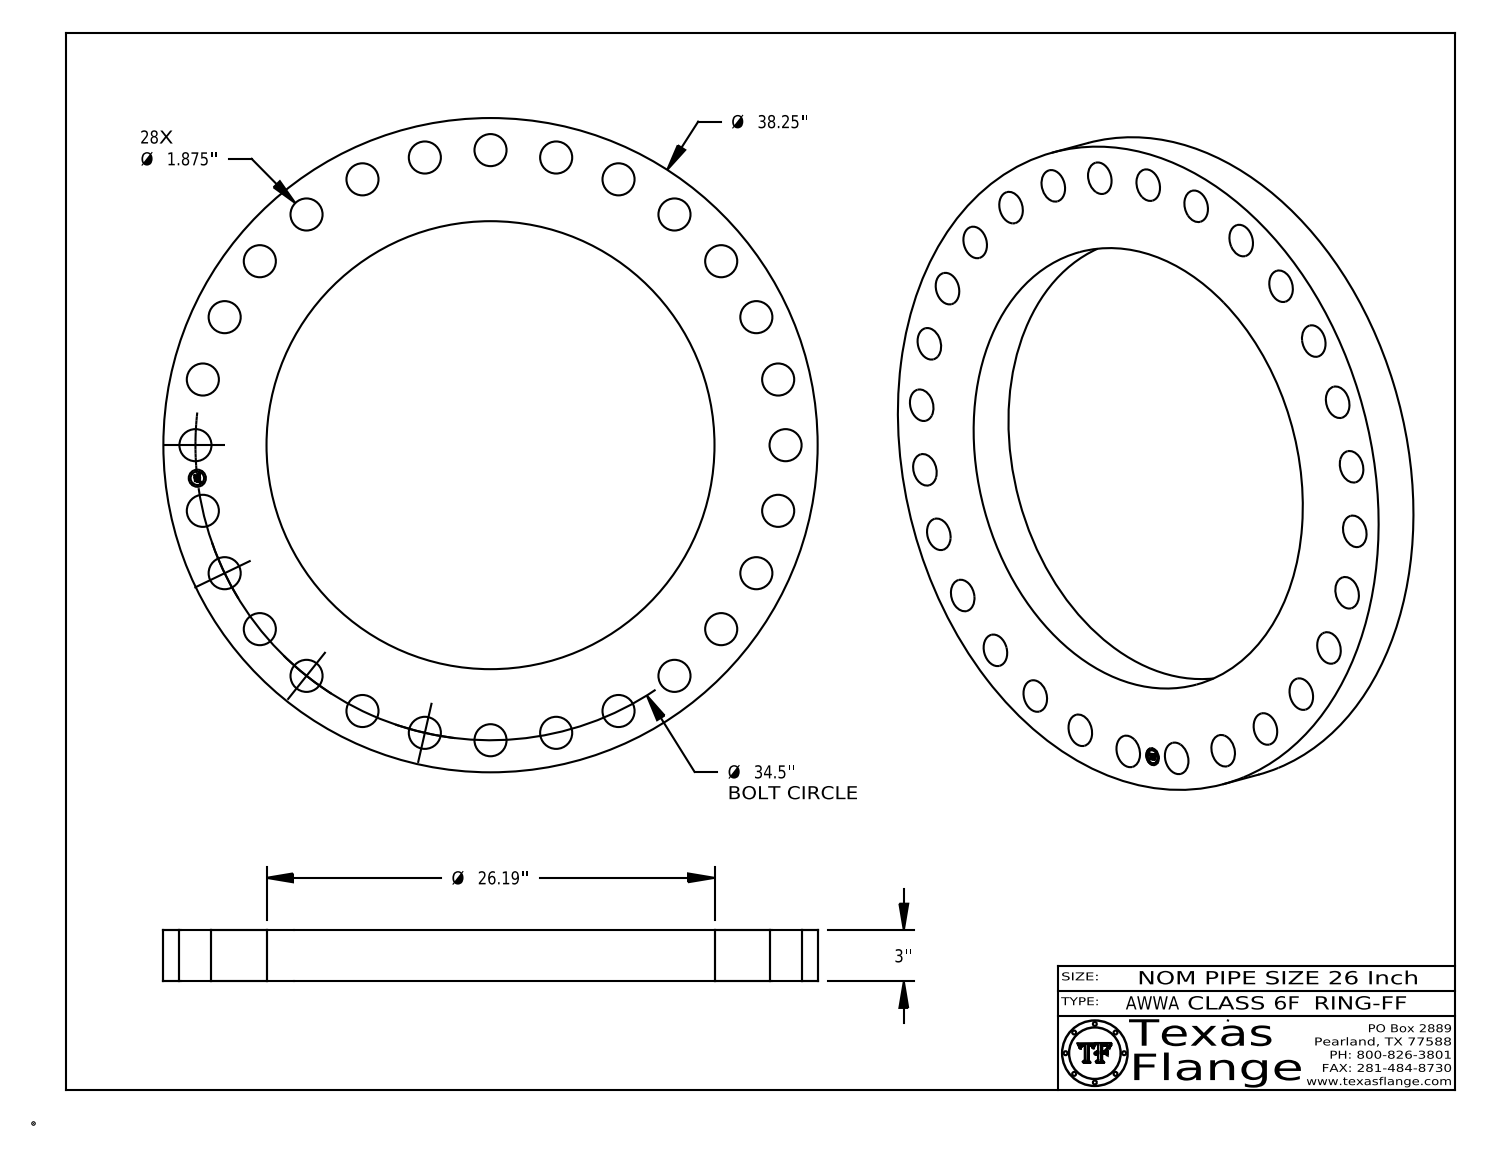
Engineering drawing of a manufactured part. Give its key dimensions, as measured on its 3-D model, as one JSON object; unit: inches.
{"part_name": "AWWA Class 6F-RING-FF", "step_written_by": "CATIA V5 STEP AP214 (AUTOMOTIVE_DESIGN)", "units": "inches", "bodies": {"solids": 1, "faces": 447, "planar": 367, "cylindrical": 80, "other": 0}, "overall_size": [38.25, 38.25, 3], "volume_in3": 1599, "surface_area_in2": 2168, "round_holes": [[1.875, 28], [1, 1], [26.19, 1]], "round_bosses_or_shafts": [[0.061, 8], [38.25, 1], [0.788, 1]], "face_to_face_distances": [3, 0.015, 2.985, 0.298, 0.292, 0.054, 0.193, 0.248, 0.044, 0.15], "hole_center_spacings": [17.25, 26.973, 34.283, 14.969, 18.355, 32.564, 33.635, 11.394]}
